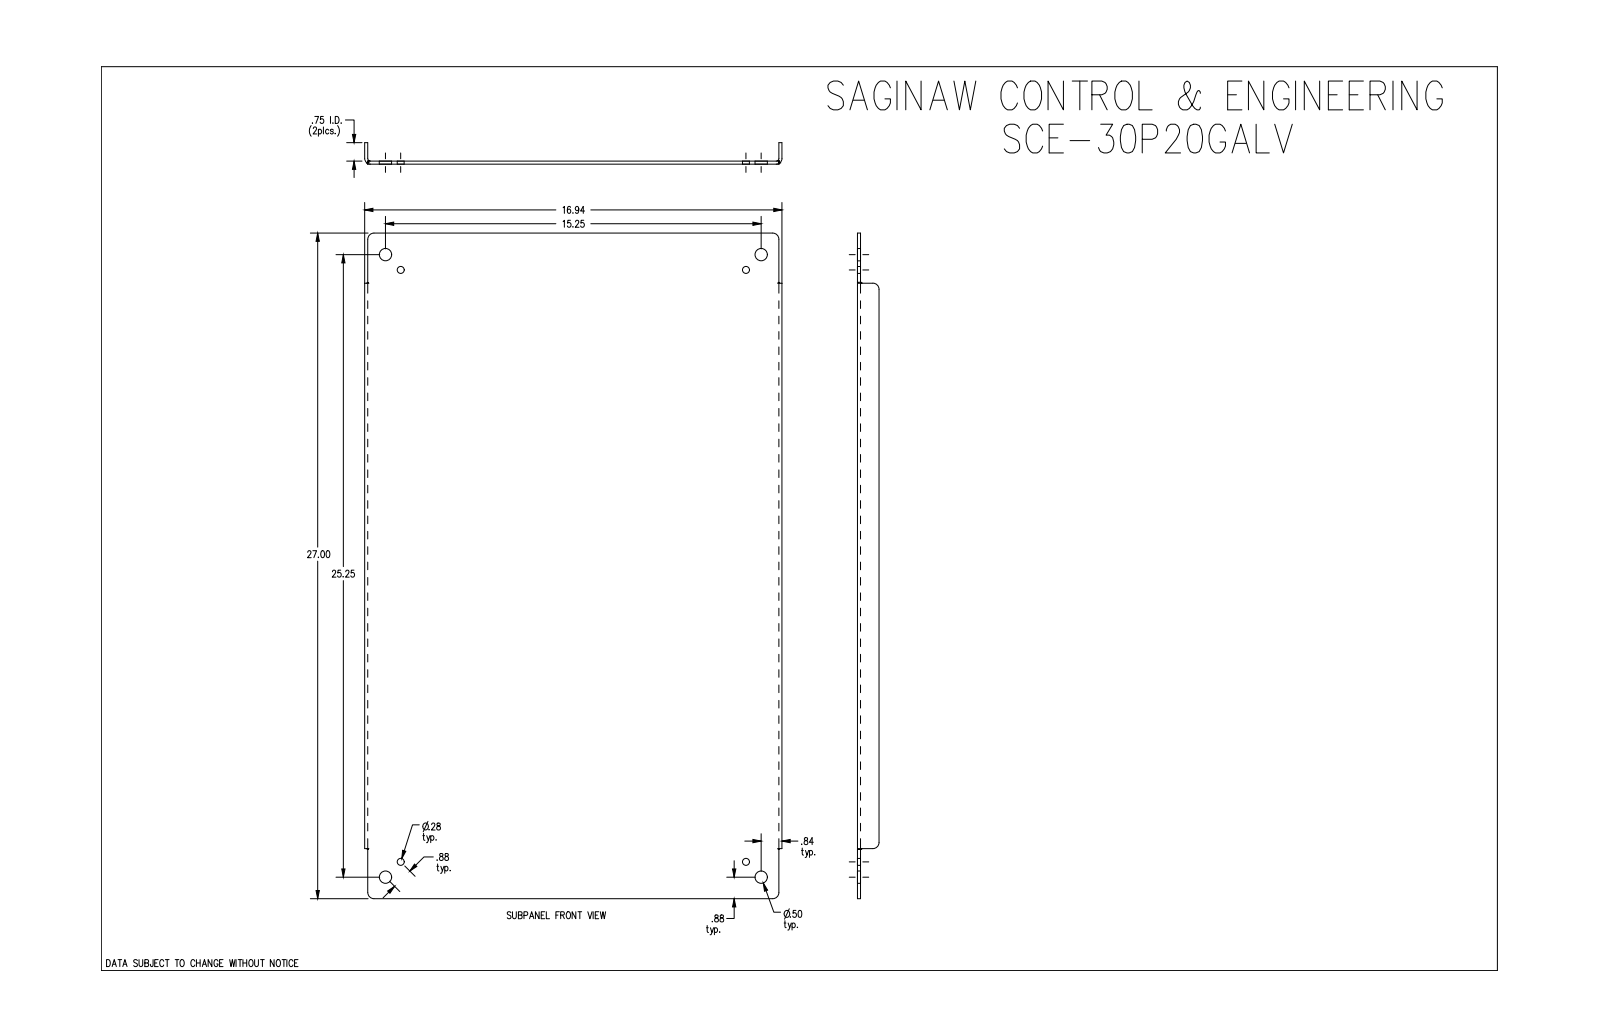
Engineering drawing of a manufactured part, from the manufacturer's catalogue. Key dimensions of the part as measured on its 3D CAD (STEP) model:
Part name (STEP PRODUCT): SCE-30P20GALV
STEP written by: SolidWorks 2019 (CONFIG_CONTROL_DESIGN)
Units: inches
Bodies: 1 solid, 50 faces (18 planar, 20 cylindrical, 12 other)
Overall size (bounding box): 27 × 16.938 × 0.875
Volume: 60.77 in³ · Surface area: 984.7 in²
Round holes (diameter × count): ⌀0.281 ×4, ⌀0.5 ×4
Partial cylindrical surfaces — rounded edges, fillets, slot ends (radius × count): R0.25 ×6, R0.112 ×2, R0.237 ×2
Main face-to-face distances: 0.125, 0.125, 16.813, 16.687, 16.938, 0.75, 0.875, 27, 2.031, 24.969
Hole centre spacings: 0.875, 14.644, 24.639, 28.649, 14.013, 15.25, 24.013, 25.25
